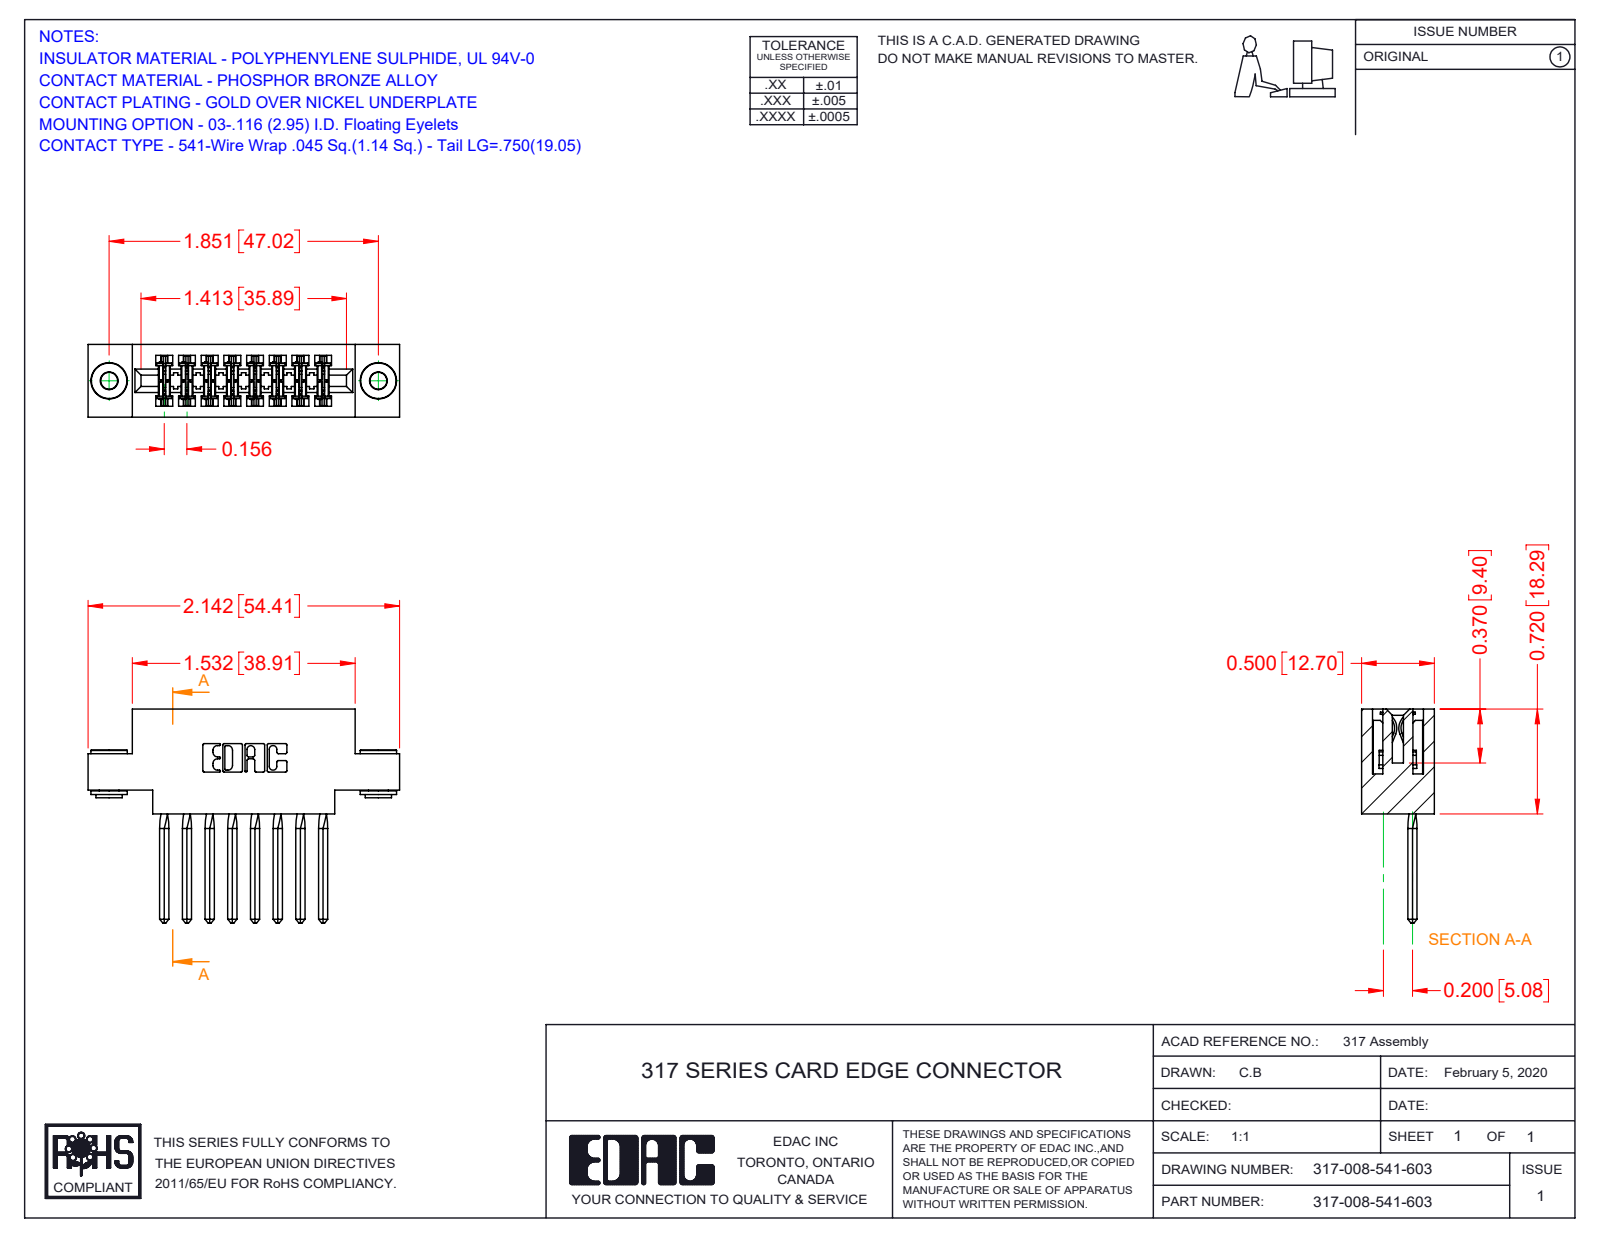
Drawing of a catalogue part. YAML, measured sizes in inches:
part_name: "317 Part_.156 Dia - TH; 345-250-002_345-250-002-102; 317-008-541-603; 317-290-002_541"
step_written_by: "SolidWorks 2016 (CONFIG_CONTROL_DESIGN)"
units: inches
bodies: {solids: 11, faces: 1356, planar: 1060, cylindrical: 256, other: 40}
overall_size: [2.142, 1.47, 0.5]
volume: 0.476
surface_area: 15.65
round_holes:
  - {diameter: 0.116, count: 2}
  - {diameter: 0.156, count: 2}
round_bosses_or_shafts:
  - {diameter: 0.25, count: 2}
  - {diameter: 0.18, count: 2}
  - {diameter: 0.136, count: 2}
partial_cylinders:
  - {radius: 0.01, count: 22}
  - {radius: 0.015, count: 16}
  - {radius: 0.007, count: 6}
  - {radius: 0.031, count: 6}
  - {radius: 0.026, count: 3}
  - {radius: 0.095, count: 2}
  - {radius: 0.1, count: 2}
  - {radius: 0.11, count: 2}
face_to_face_distances: [0.5, 0.075, 0.425, 0.11, 0.065, 0.22, 0.156, 0.331, 0.305, 0.116]
hole_center_spacings: [1.851]
